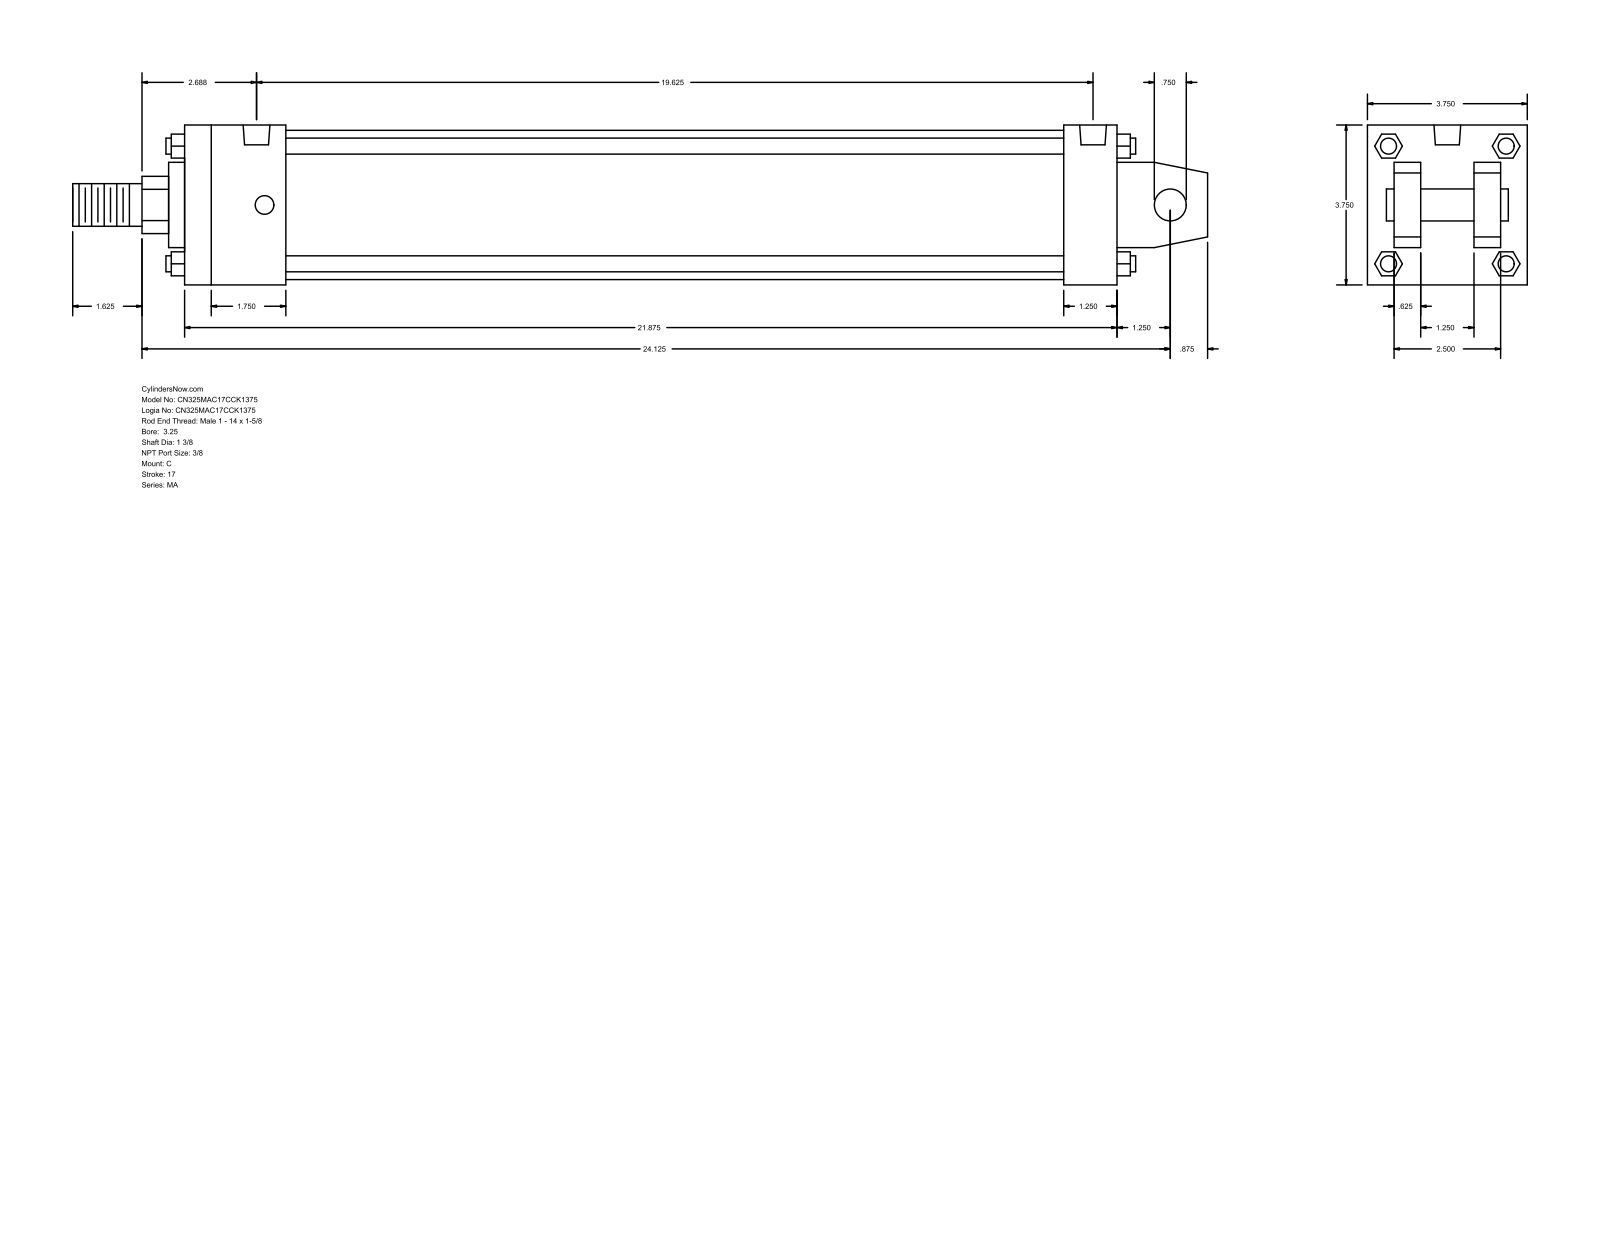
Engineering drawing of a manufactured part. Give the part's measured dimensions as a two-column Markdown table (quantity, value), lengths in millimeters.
| quantity | value |
| --- | --- |
| part name | MA_C__0325_1.375 |
| STEP written by | GSSL Pune (CONFIG_CONTROL_DESIGN) |
| units | millimeters |
| bodies | 0 solids, 139 faces (108 planar, 31 cylindrical, 0 other) |
| overall size | 676.27 × 95.25 × 95.25 |
| round holes (diameter × count) | 11.11 × 4, 15.93 × 2 |
| round bosses / shafts (diameter × count) | 9.53 × 4, 88.9 × 1, 50.8 × 1, 34.92 × 1, 25.4 × 1, 19.05 × 1 |
| partial cylindrical surfaces (radius × count) | 17.06 × 1 |
| main face-to-face distances | 95.24, 15.87, 63.5, 555.62, 31.74, 79.37, 47.63, 523.87, 31.75, 60.32 |
| hole center spacings | 488.95, 4.76, 4.77, 493.71, 493.72, 498.48 |
